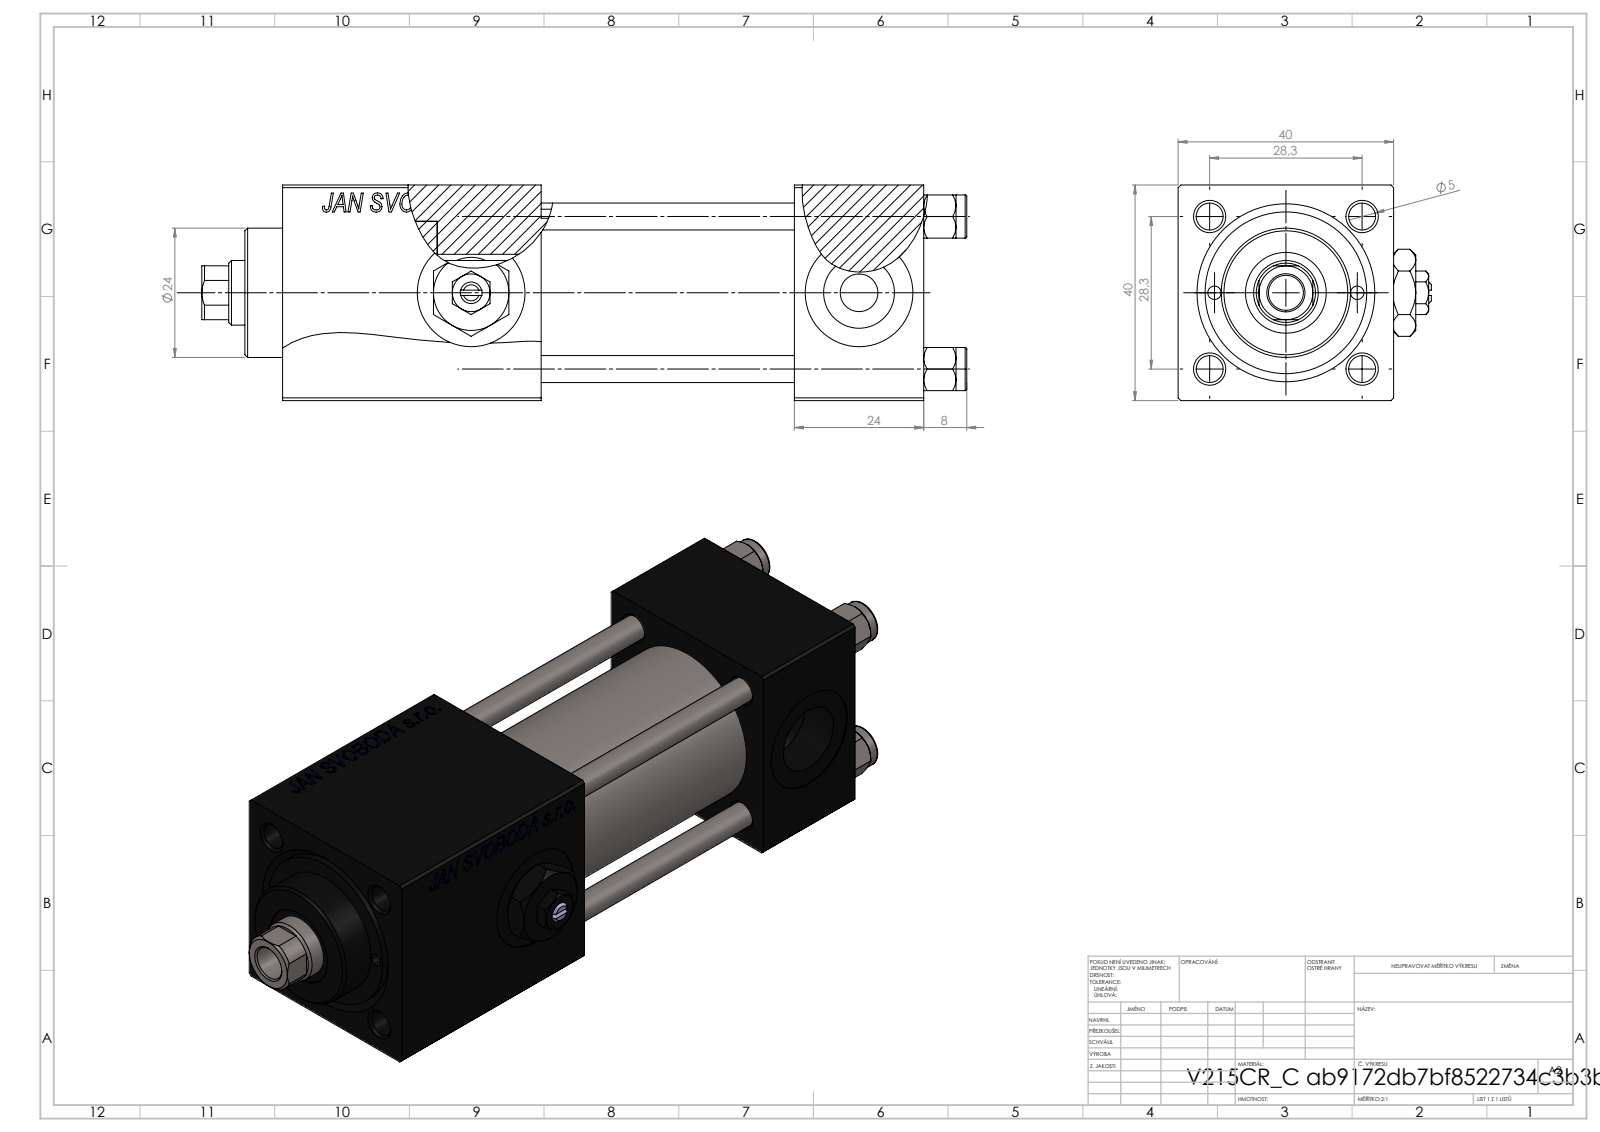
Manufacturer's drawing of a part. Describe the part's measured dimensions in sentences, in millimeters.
The part is named "Zatka_pro_OIL_PORT; V215_VC_A; V215CR_VCP_C; V215CR_C_TYCINKA (+2 more)". Its 3-D file was written by "SolidWorks 2019 (CONFIG_CONTROL_DESIGN)". It is 12 solids with 1201 faces: 551 planar, 94 cylindrical and 556 other. Overall it measures 142 by 47 by 40 millimeters. Its volume is 141 941 cubic millimeters and its surface area 55 199 square millimeters. Round holes: 4 of diameter 5, 3 of diameter 20, 2 of diameter 2.5, 2 of diameter 7, 2 of diameter 13.16, 1 of diameter 6.5, 1 of diameter 12, 1 of diameter 15, 1 of diameter 25, 1 of diameter 30. Round bosses or shafts: 4 of diameter 8, 1 of diameter 31, 1 of diameter 24. Partial cylindrical surfaces (rounded edges, fillets, slot ends): 1 of radius 5.5. The main face-to-face distances are 40, 24, 90.3, 66.3, 48, 47, 71, 19.3, 119, 95. The hole center spacings are 14.18, 20.01, 28.3, 30.84, 13.25, 40.02, 26.5, 72.
